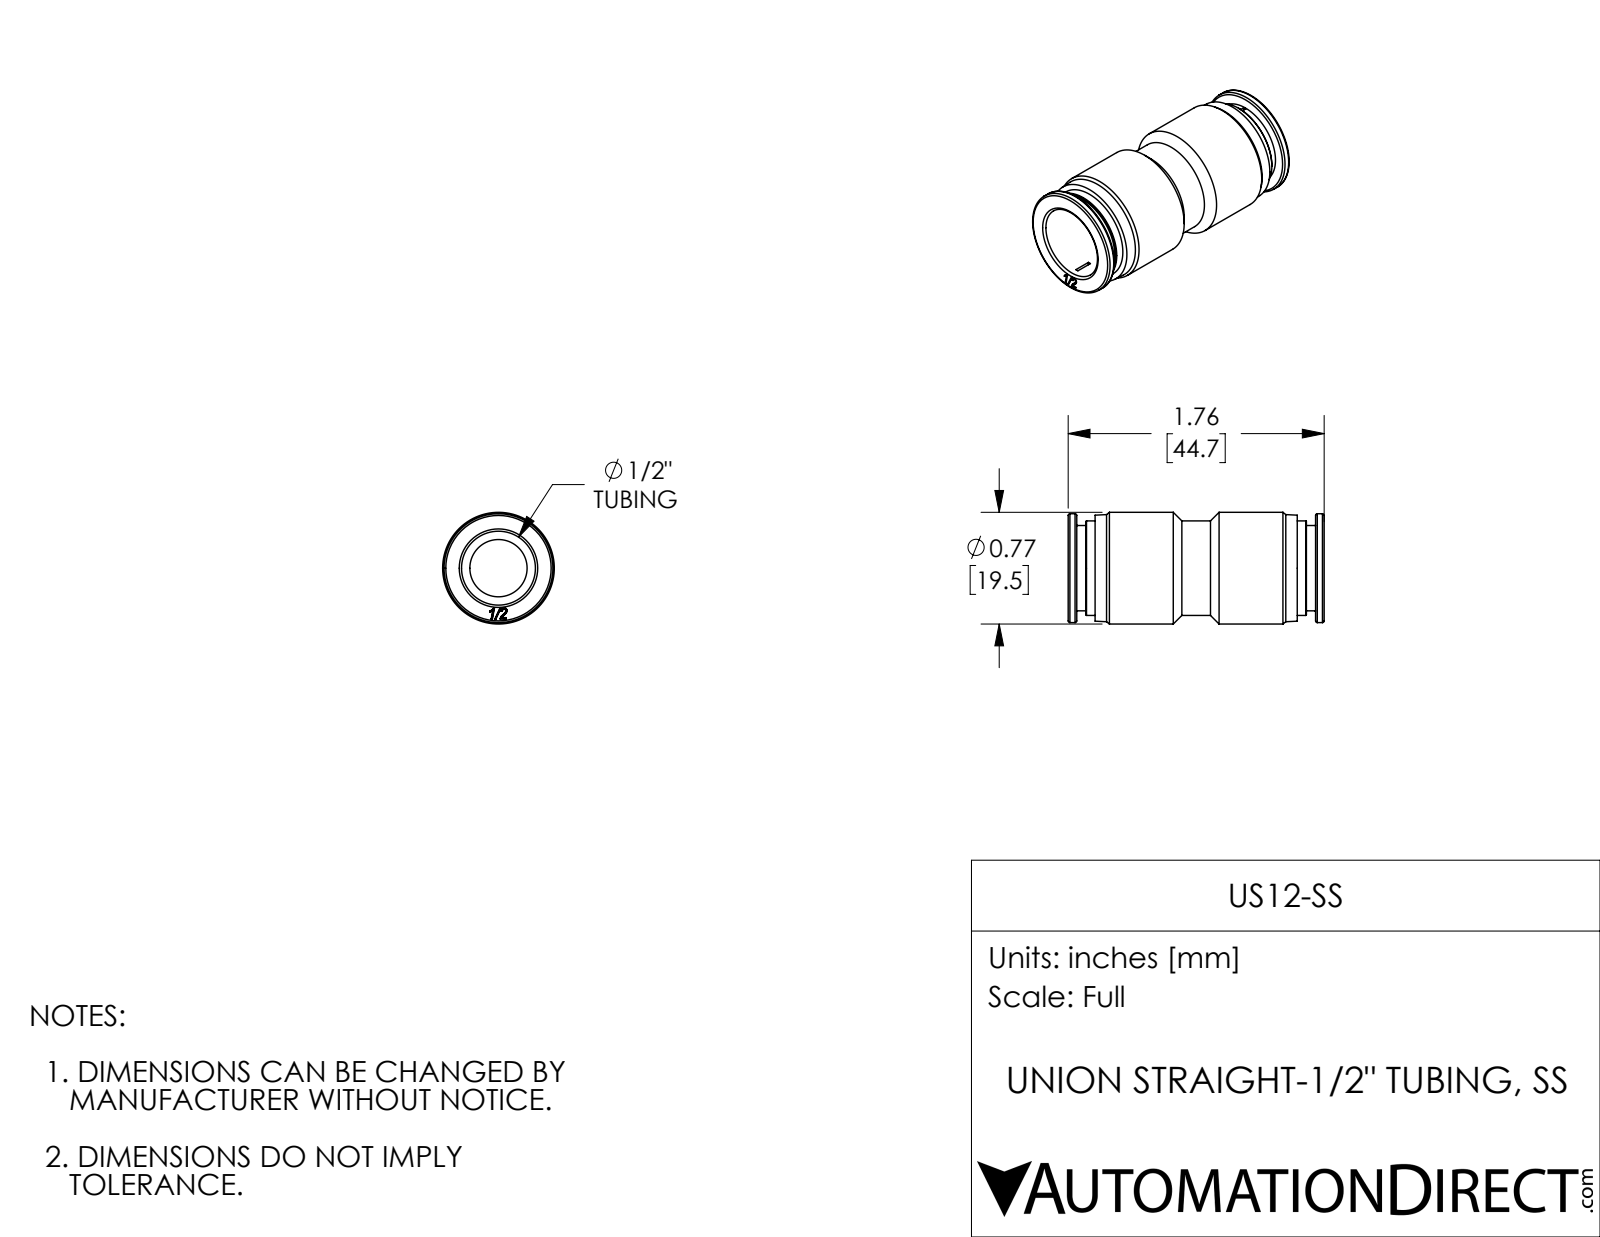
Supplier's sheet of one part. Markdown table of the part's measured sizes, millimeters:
| quantity | value |
| --- | --- |
| part name | US12-SS |
| STEP written by | SolidWorks 2017 (AUTOMOTIVE_DESIGN) |
| units | millimeters |
| bodies | 1 solid, 148 faces (56 planar, 28 cylindrical, 64 other) |
| overall size | 44.7 × 19.5 × 19.5 |
| volume | 6 160 mm³ |
| surface area | 5 536 mm² |
| round holes (diameter × count) | 10 × 1, 12.9 × 1, 15.1 × 1 |
| round bosses / shafts (diameter × count) | 19.5 × 1, 19 × 1, 16.5 × 1, 14.9 × 1 |
| main face-to-face distances | 1.5, 21.6, 43.2, 38.5, 40, 4.7, 3.2, 44.7, 23.1, 20.1 |
